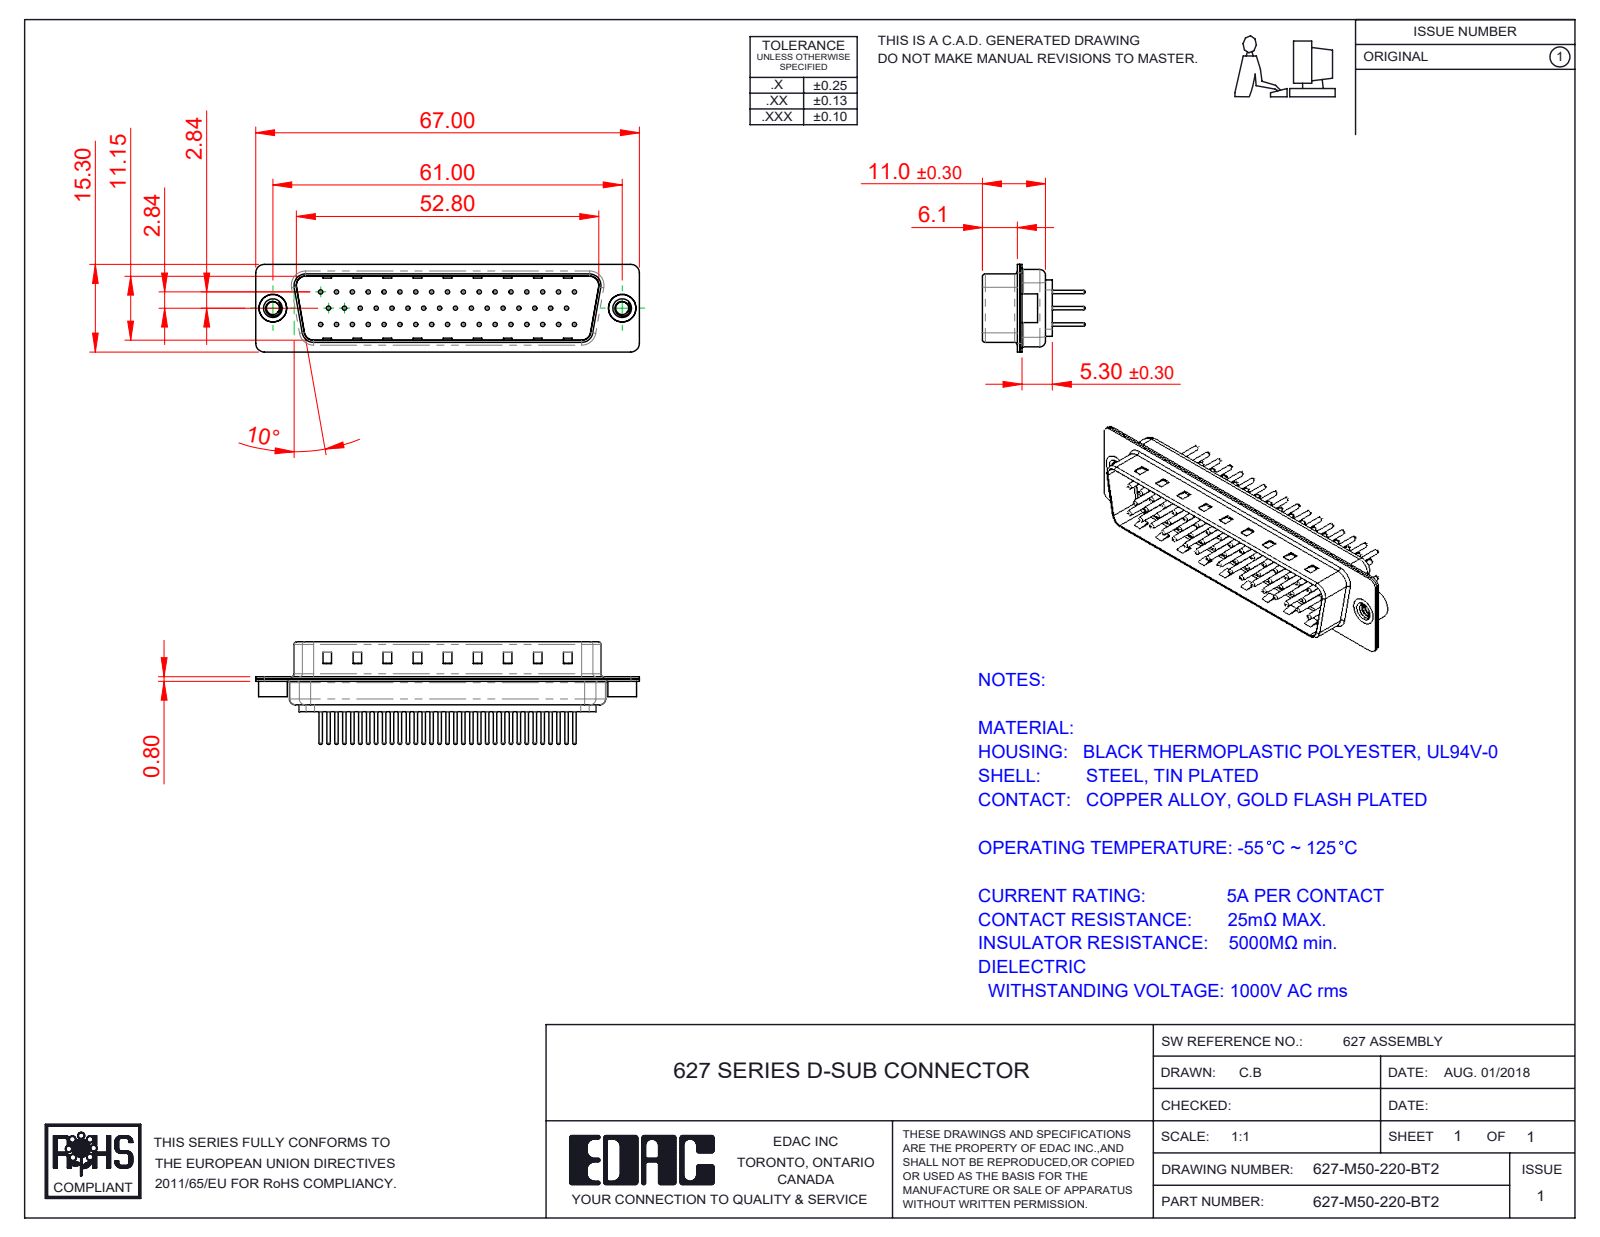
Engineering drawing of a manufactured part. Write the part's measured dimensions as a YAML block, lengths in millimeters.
part_name: "627M Contact Row 2_20; 627M Shell Front_50 Contacts; 627M Housing_50 Contacts; 627M 4-40 Threaded Rivet (+4 more)"
step_written_by: "SolidWorks 2020 (CONFIG_CONTROL_DESIGN)"
units: millimeters
bodies: {solids: 55, faces: 2262, planar: 553, cylindrical: 841, other: 868}
overall_size: [67, 17.9, 15.3]
volume: 4525
surface_area: 10699
round_holes:
  - {diameter: 0.75, count: 50}
  - {diameter: 1.6, count: 50}
  - {diameter: 2, count: 50}
  - {diameter: 2.26, count: 2}
  - {diameter: 4, count: 2}
  - {diameter: 4.8, count: 2}
round_bosses_or_shafts:
  - {diameter: 1.5, count: 50}
  - {diameter: 0.6, count: 50}
  - {diameter: 5, count: 2}
  - {diameter: 4.9, count: 2}
partial_cylinders:
  - {radius: 1.5, count: 16}
  - {radius: 2, count: 12}
  - {radius: 0.5, count: 8}
  - {radius: 1.6, count: 8}
  - {radius: 0.25, count: 4}
  - {radius: 0.6, count: 4}
  - {radius: 0.65, count: 4}
  - {radius: 0.9, count: 4}
face_to_face_distances: [0.4, 11.55, 5.7, 6.1, 0.78, 0.77, 12.33, 12.32, 13.1, 5.3]
hole_center_spacings: [3.16, 2.77, 5.54, 8.31, 11.08, 13.85, 16.62, 5.03]
